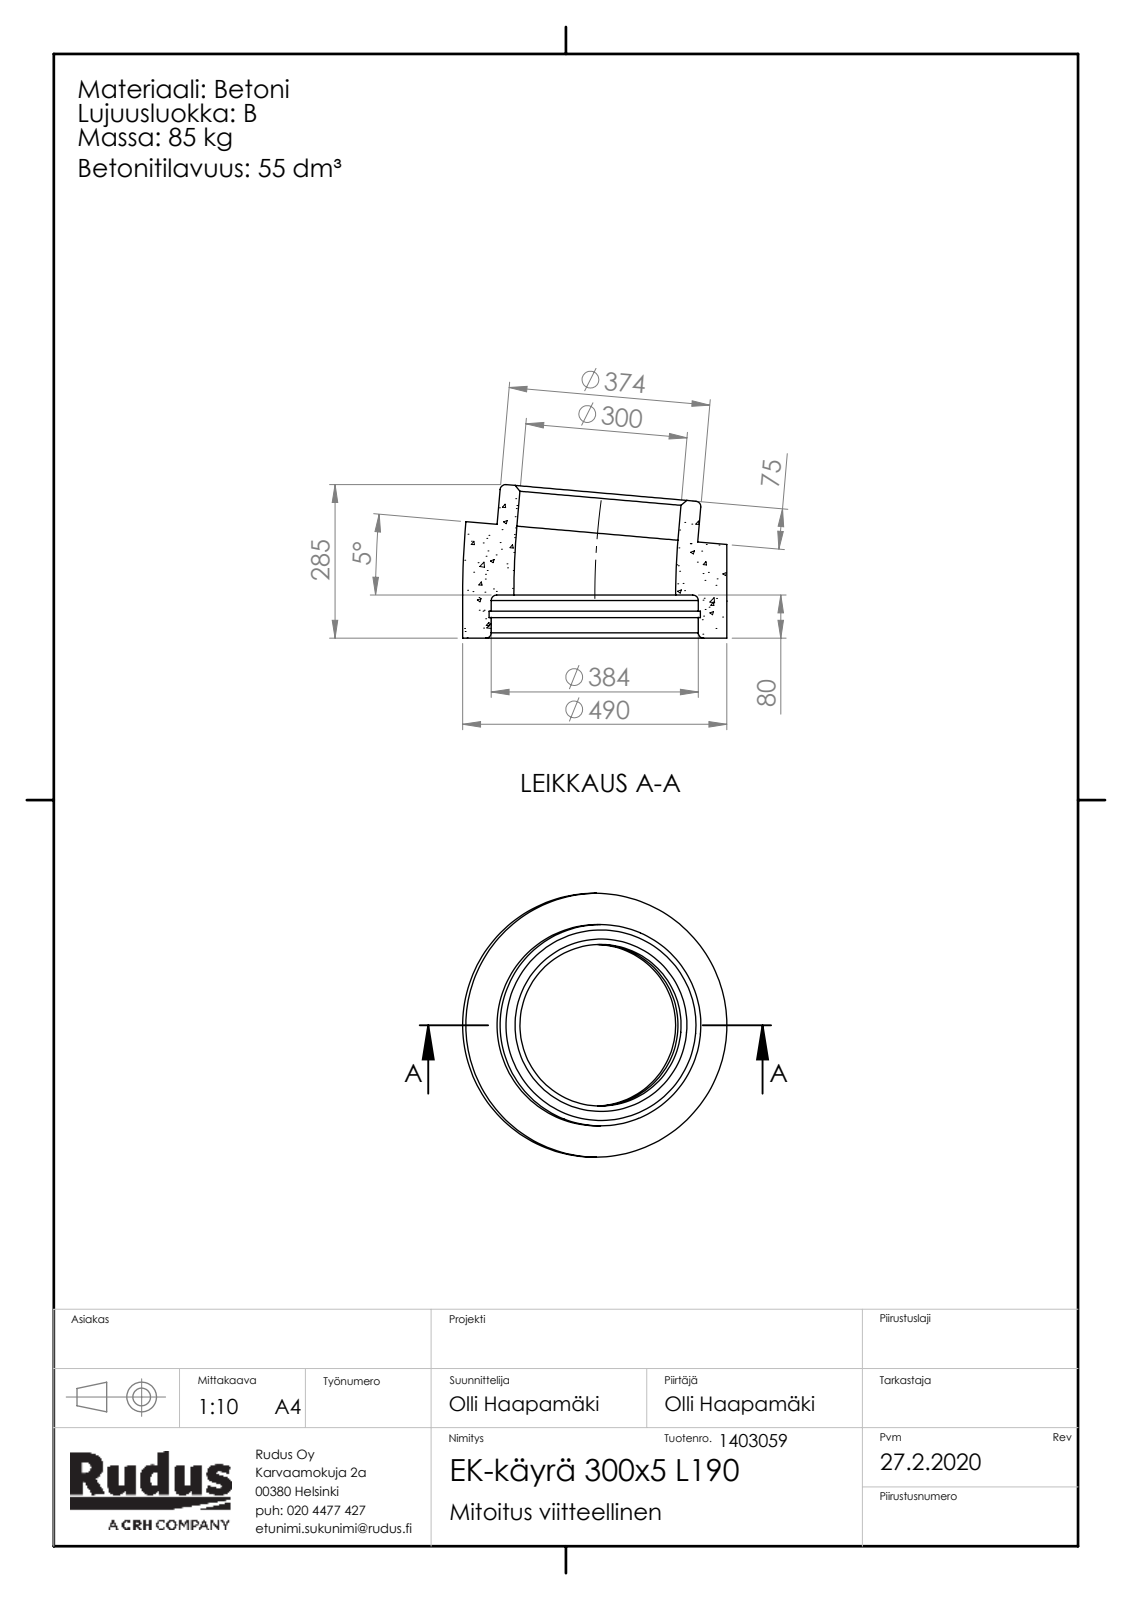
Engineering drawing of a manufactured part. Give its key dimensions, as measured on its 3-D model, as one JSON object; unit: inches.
{"part_name": "EK-osa-runko-käyrä; Rudus 1403059 EK-käyrä 300x5 L190", "step_written_by": "SolidWorks 2019 (CONFIG_CONTROL_DESIGN)", "units": "inches", "bodies": {"solids": 1, "faces": 100, "planar": 8, "cylindrical": 21, "other": 71}, "overall_size": [19.291, 19.291, 11.221], "volume_in3": 1348, "surface_area_in2": 1377, "round_holes": [[11.811, 1], [15.118, 1], [15.433, 1]], "round_bosses_or_shafts": [[19.291, 1], [14.709, 1]], "partial_cylinders_radius": [[9.528, 1]], "face_to_face_distances": [3.15, 2.951, 1.496, 1.654, 1.969, 0.472, 1.181, 1.984, 0.488, 0.015]}
